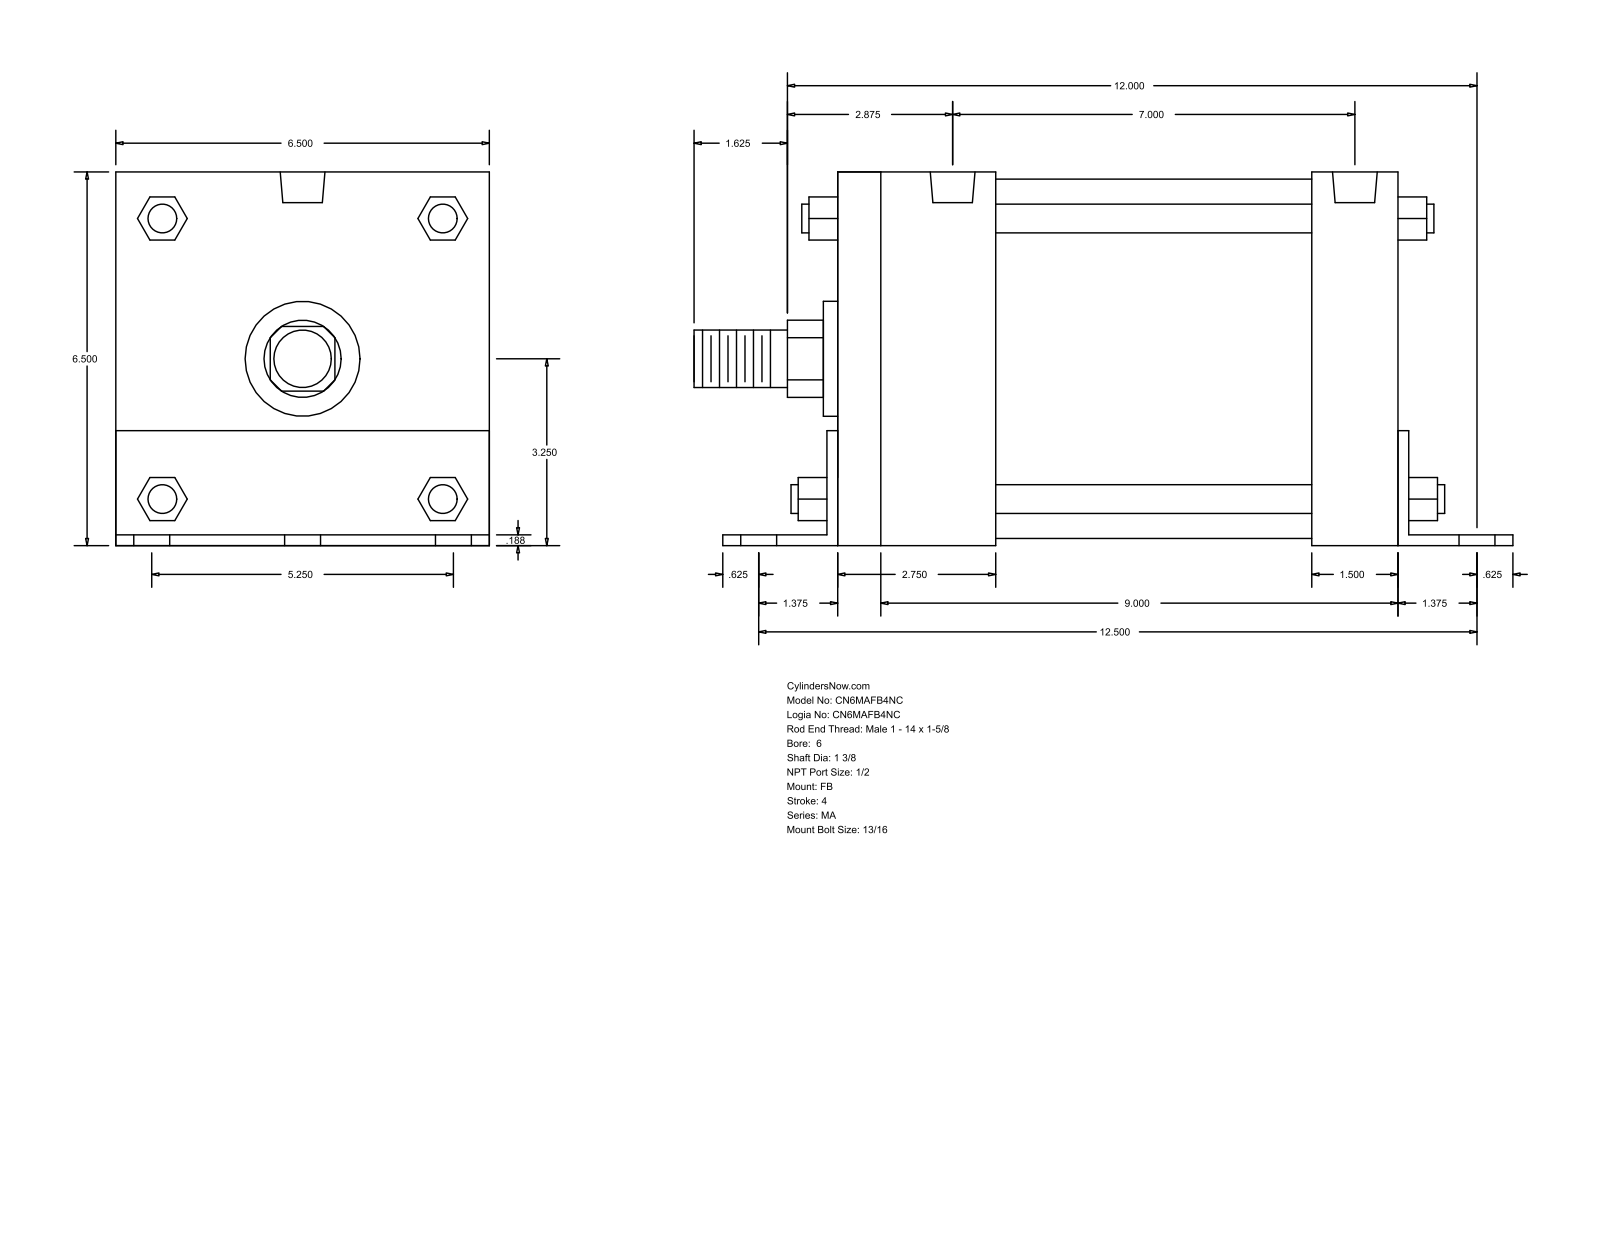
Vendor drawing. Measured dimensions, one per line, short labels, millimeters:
name: MA_FB__0600_1.375
written by: GSSL Pune (CONFIG_CONTROL_DESIGN)
unit: mm
bodies: 0 solids, 140 faces (105 planar, 35 cylindrical, 0 other)
size: 358.77 × 165.15 × 165.1
holes: 6× ⌀20.64, 4× ⌀17.46, 2× ⌀19.77
bosses: 4× ⌀12.7, 1× ⌀158.75, 1× ⌀50.8, 1× ⌀34.92, 1× ⌀25.4
rounds: 1× R17.06, 1× R32.05
face distances: 165.1, 4.76, 244.47, 165.15, 4.71, 160.39, 4.77, 38.1, 42.86, 254
hole spacings: 66.67, 321.31, 314.32, 83.82, 85.78, 108.6, 133.34, 174.62
